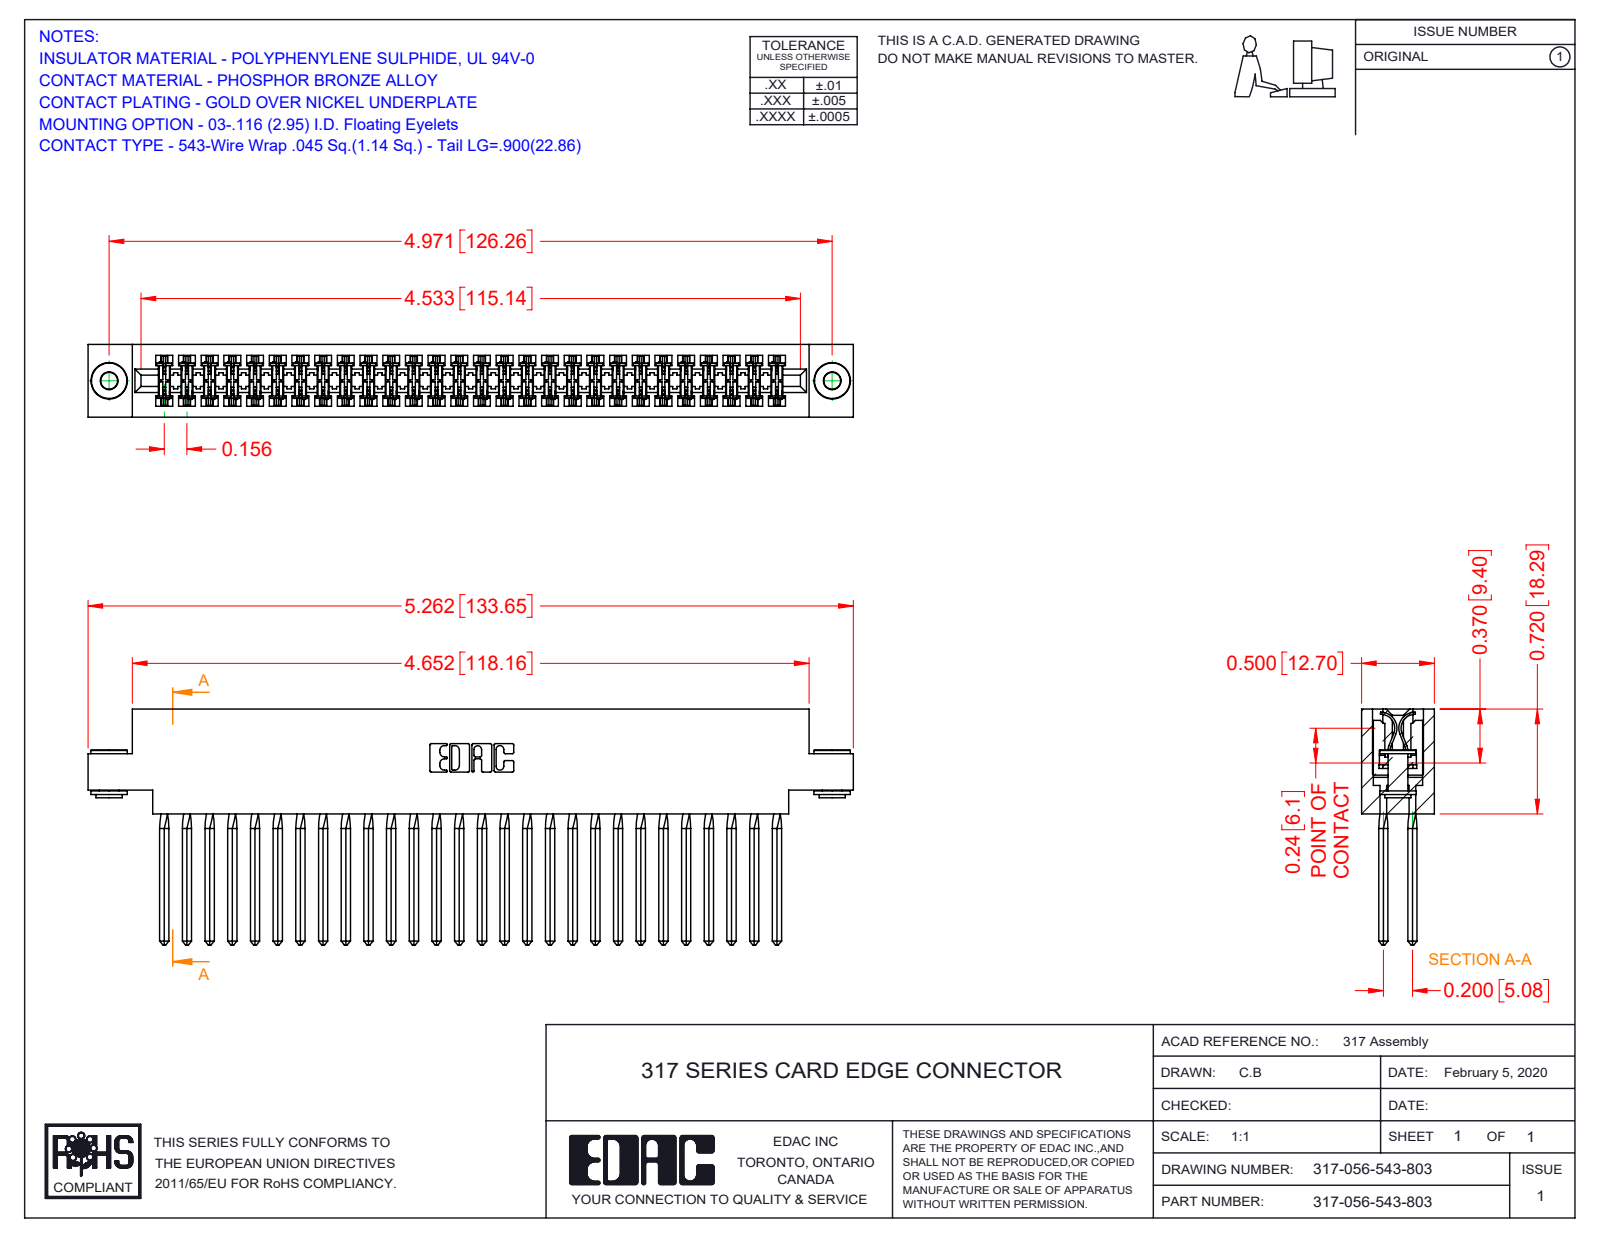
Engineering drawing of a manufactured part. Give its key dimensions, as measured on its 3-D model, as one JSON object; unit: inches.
{"part_name": "317 Part_.156 Dia - TH; 317-056-543-803; 317-290-001_543; 345-250-002_345-250-002-102", "step_written_by": "SolidWorks 2016 (CONFIG_CONTROL_DESIGN)", "units": "inches", "bodies": {"solids": 59, "faces": 5124, "planar": 4156, "cylindrical": 736, "other": 232}, "overall_size": [5.262, 1.62, 0.5], "volume_in3": 1.358, "surface_area_in2": 51.81, "round_holes": [[0.116, 2], [0.156, 2]], "round_bosses_or_shafts": [[0.25, 2], [0.18, 2], [0.136, 2]], "partial_cylinders_radius": [[0.015, 112], [0.01, 22], [0.007, 6], [0.031, 6], [0.026, 3], [0.095, 2], [0.1, 2], [0.11, 2]], "face_to_face_distances": [0.5, 0.075, 0.425, 0.35, 0.11, 0.195, 0.094, 0.2, 0.72, 0.115], "hole_center_spacings": [4.971]}
